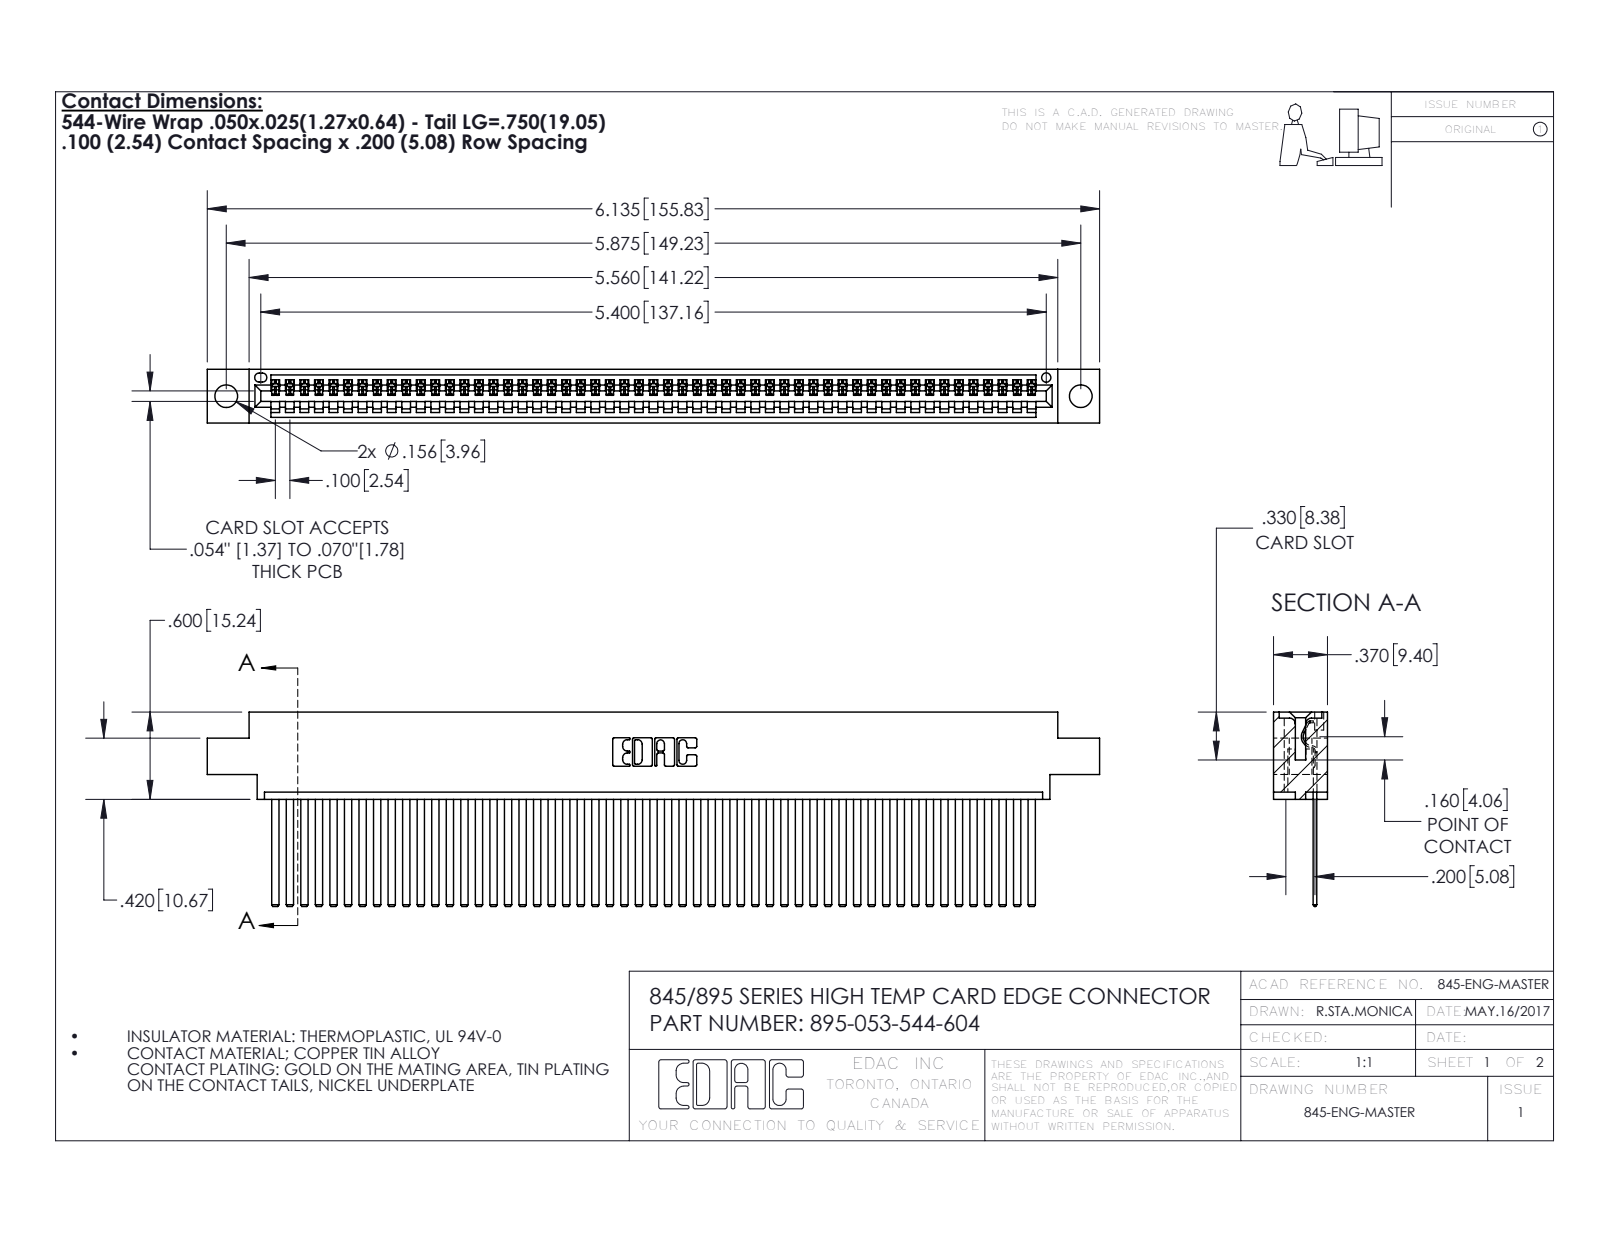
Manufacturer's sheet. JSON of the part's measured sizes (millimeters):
{"part_name": "395-053-544-604; 345 Part_0.170 Offset - 0.156 Dia-TH; 345-292-001_345-293-144", "step_written_by": "SolidWorks 2016 (CONFIG_CONTROL_DESIGN)", "units": "millimeters", "bodies": {"solids": 54, "faces": 2886, "planar": 1992, "cylindrical": 894, "other": 0}, "overall_size": [155.8, 34, 9.4], "volume_mm3": 15300, "surface_area_mm2": 22260, "round_holes": [[4, 2], [1.6, 1]], "partial_cylinders_radius": [[0.2, 106], [0.3, 22], [0.2, 6], [0.8, 6], [0.7, 3], [0.8, 2], [1, 2], [0.4, 1]], "face_to_face_distances": [1.8, 7.6, 0.6, 2.5, 6.9, 9.4, 5.1, 5.7, 4.4, 3.8], "hole_center_spacings": [6.9, 143.2, 149.2]}
